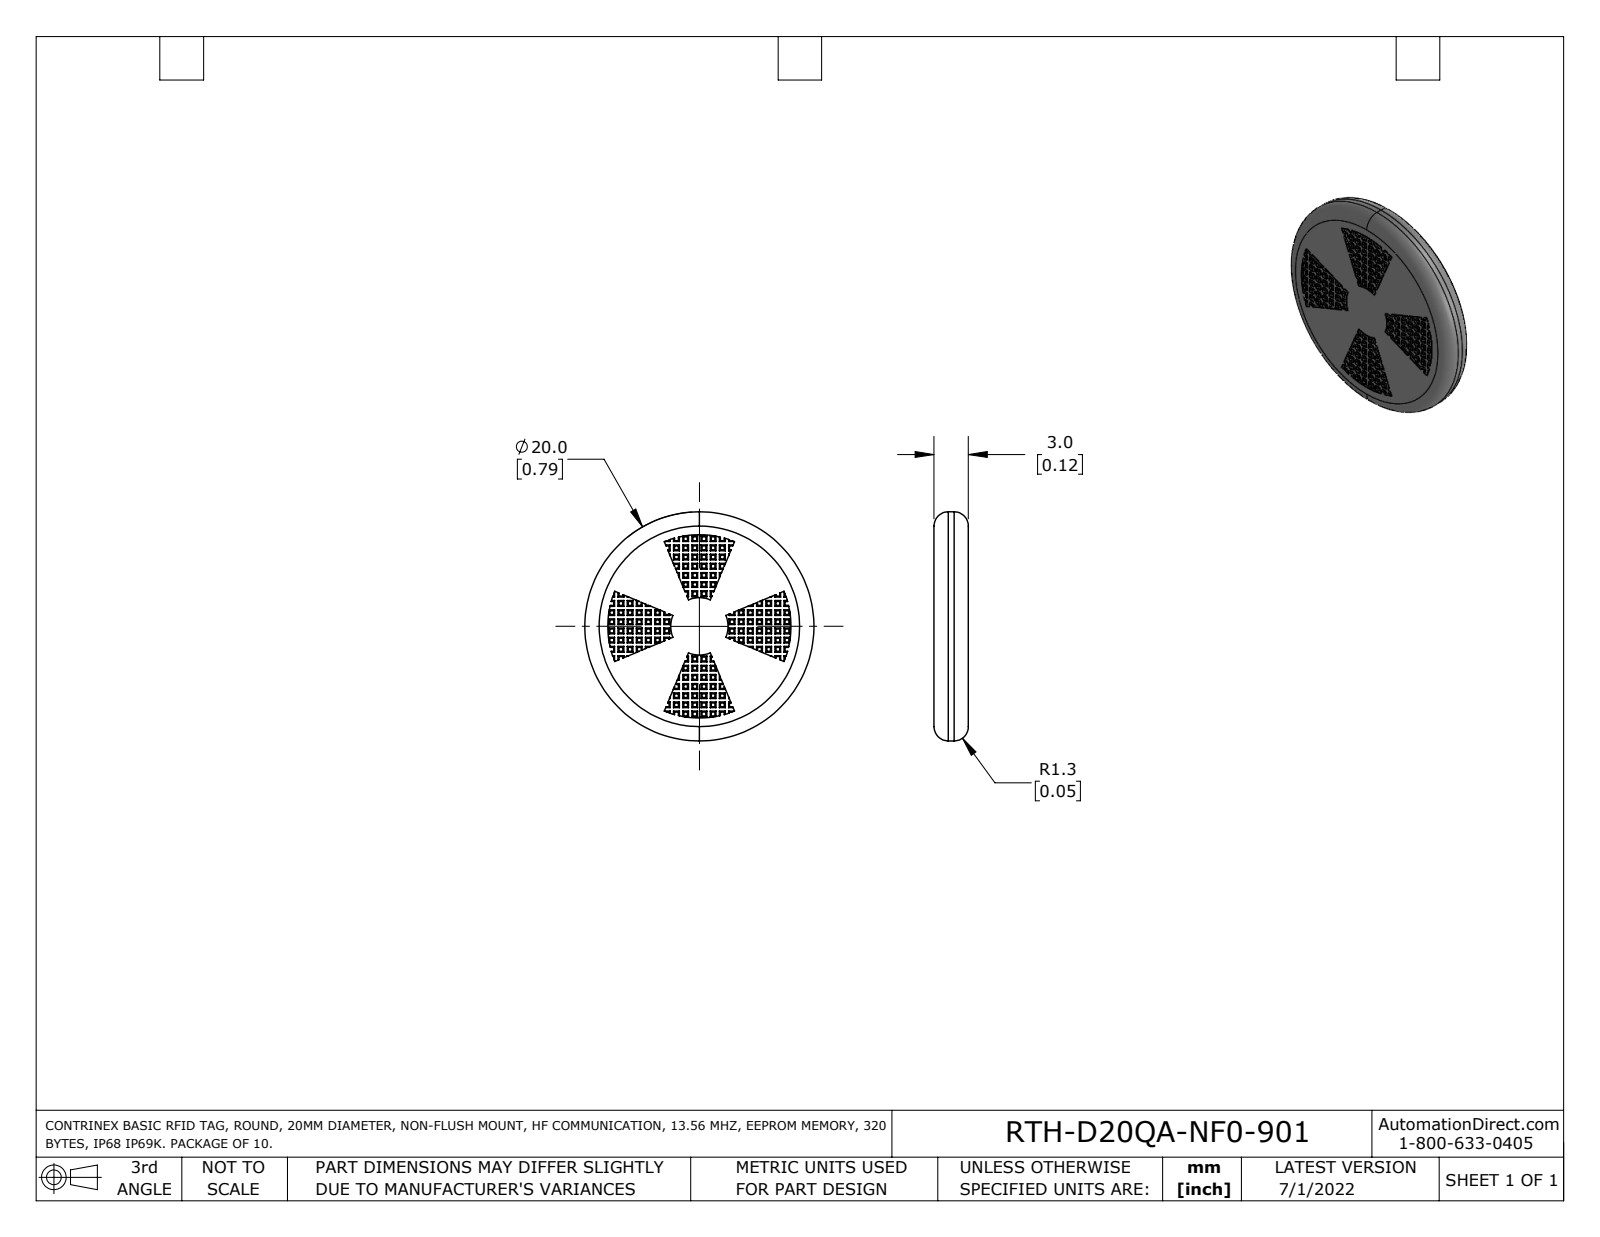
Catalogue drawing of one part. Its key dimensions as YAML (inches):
part_name: "RTH-D20QA-NC0"
step_written_by: "SolidWorks 2021 (AUTOMOTIVE_DESIGN)"
units: inches
bodies: {solids: 1, faces: 830, planar: 798, cylindrical: 28, other: 4}
overall_size: [0.787, 0.787, 0.118]
volume: 0.054
surface_area: 1.2
round_bosses_or_shafts:
  - {diameter: 0.787, count: 1}
partial_cylinders:
  - {radius: 0.098, count: 1}
  - {radius: 0.315, count: 1}
face_to_face_distances: [0.118, 0.112, 0.027, 0.165, 0.193, 0.082, 0.055, 0.054, 0.274, 0.247]
